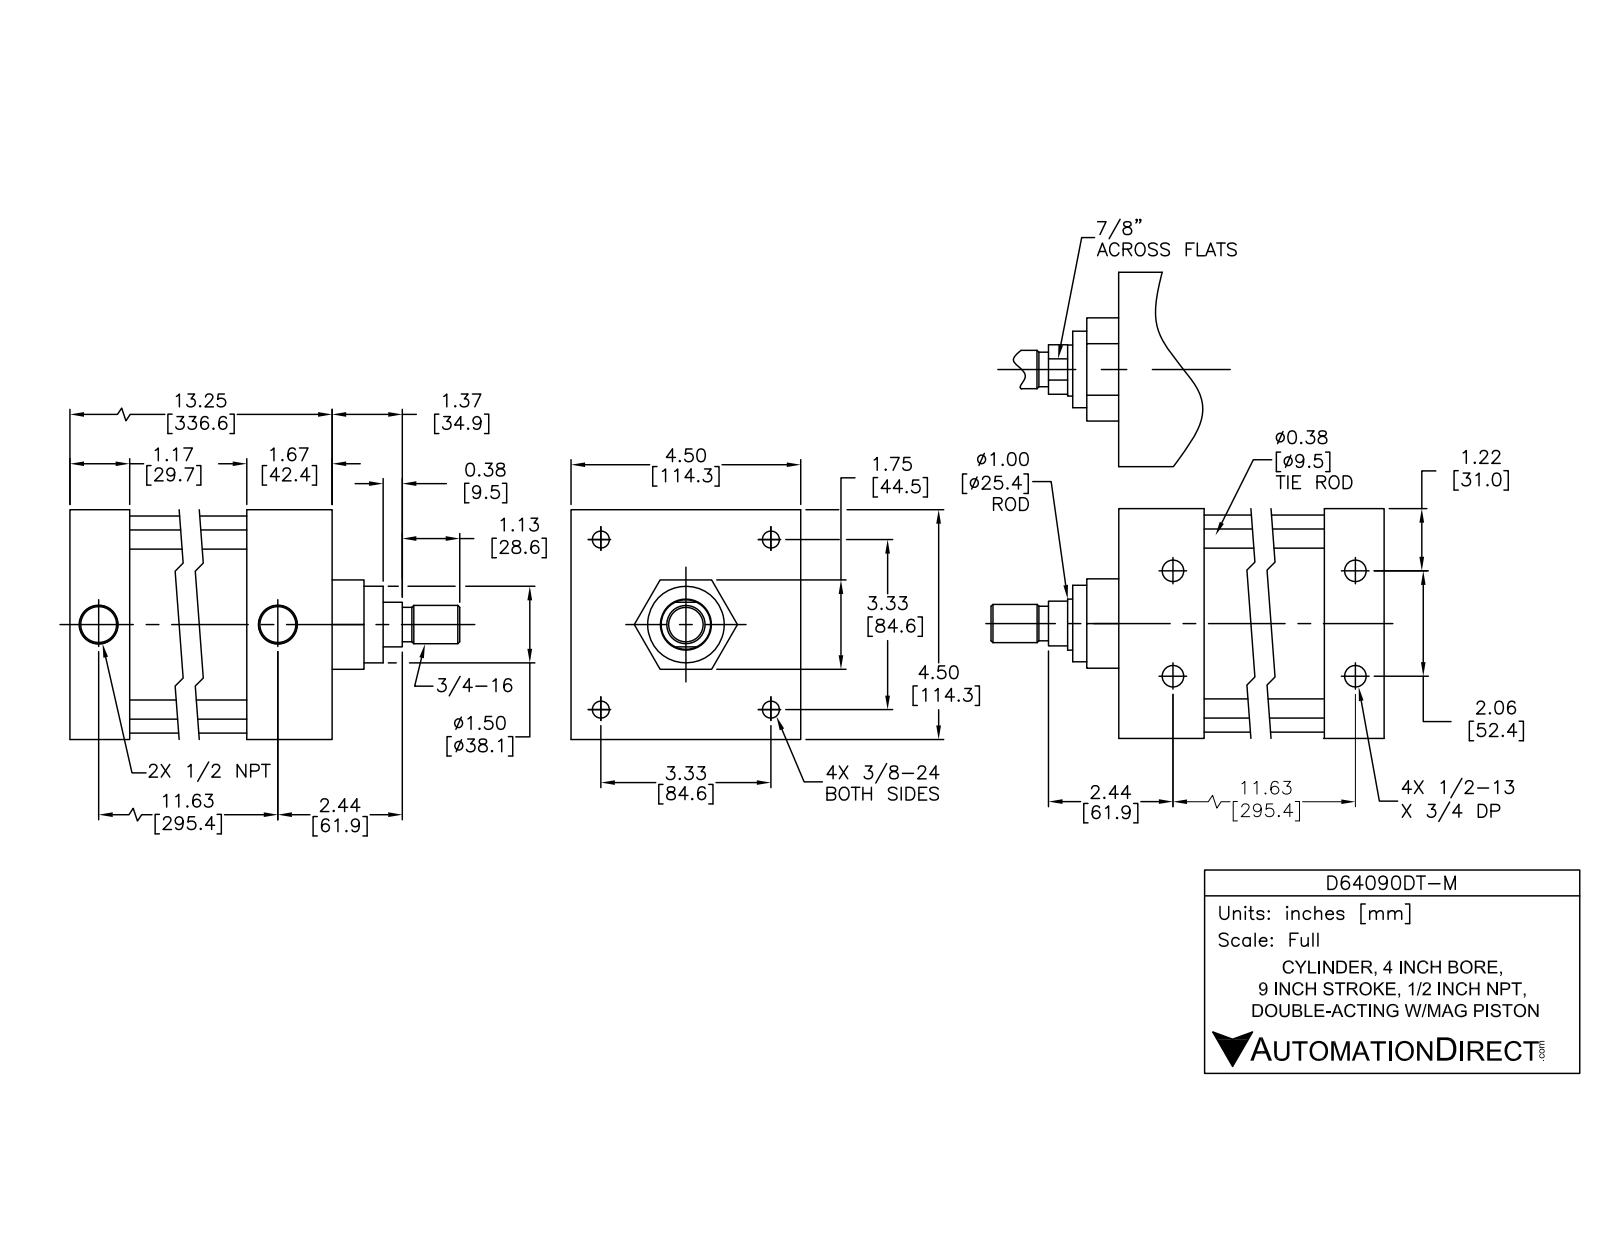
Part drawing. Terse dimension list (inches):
name: D64090DT-M; D64090DT-M PISTON; D64090DT-M BODY
written by: SolidWorks 2015 (AUTOMOTIVE_DESIGN)
unit: in
bodies: 12 solids, 303 faces (99 planar, 114 cylindrical, 90 other)
size: 15.745 × 4.5 × 4.5
volume: 102.2 in³; area: 590.3 in²
holes: 4× ⌀0.33, 4× ⌀0.406, 4× ⌀0.417, 4× ⌀0.625, 2× ⌀0.5, 2× ⌀0.766, 1× ⌀1, 1× ⌀1.003, 1× ⌀4
bosses: 4× ⌀0.609, 4× ⌀0.375, 4× ⌀0.34, 1× ⌀4.25, 1× ⌀3.997, 1× ⌀1.75, 1× ⌀0.997, 1× ⌀0.97
rounds: 4× R0.45
face distances: 4.5, 0.08, 10.326, 13.246, 1.75, 11.997, 1.249, 10.751, 1.246, 2.495
hole spacings: 1.031, 2.349, 3.322, 11.668, 11.622, 2.062, 4.698, 11.804
